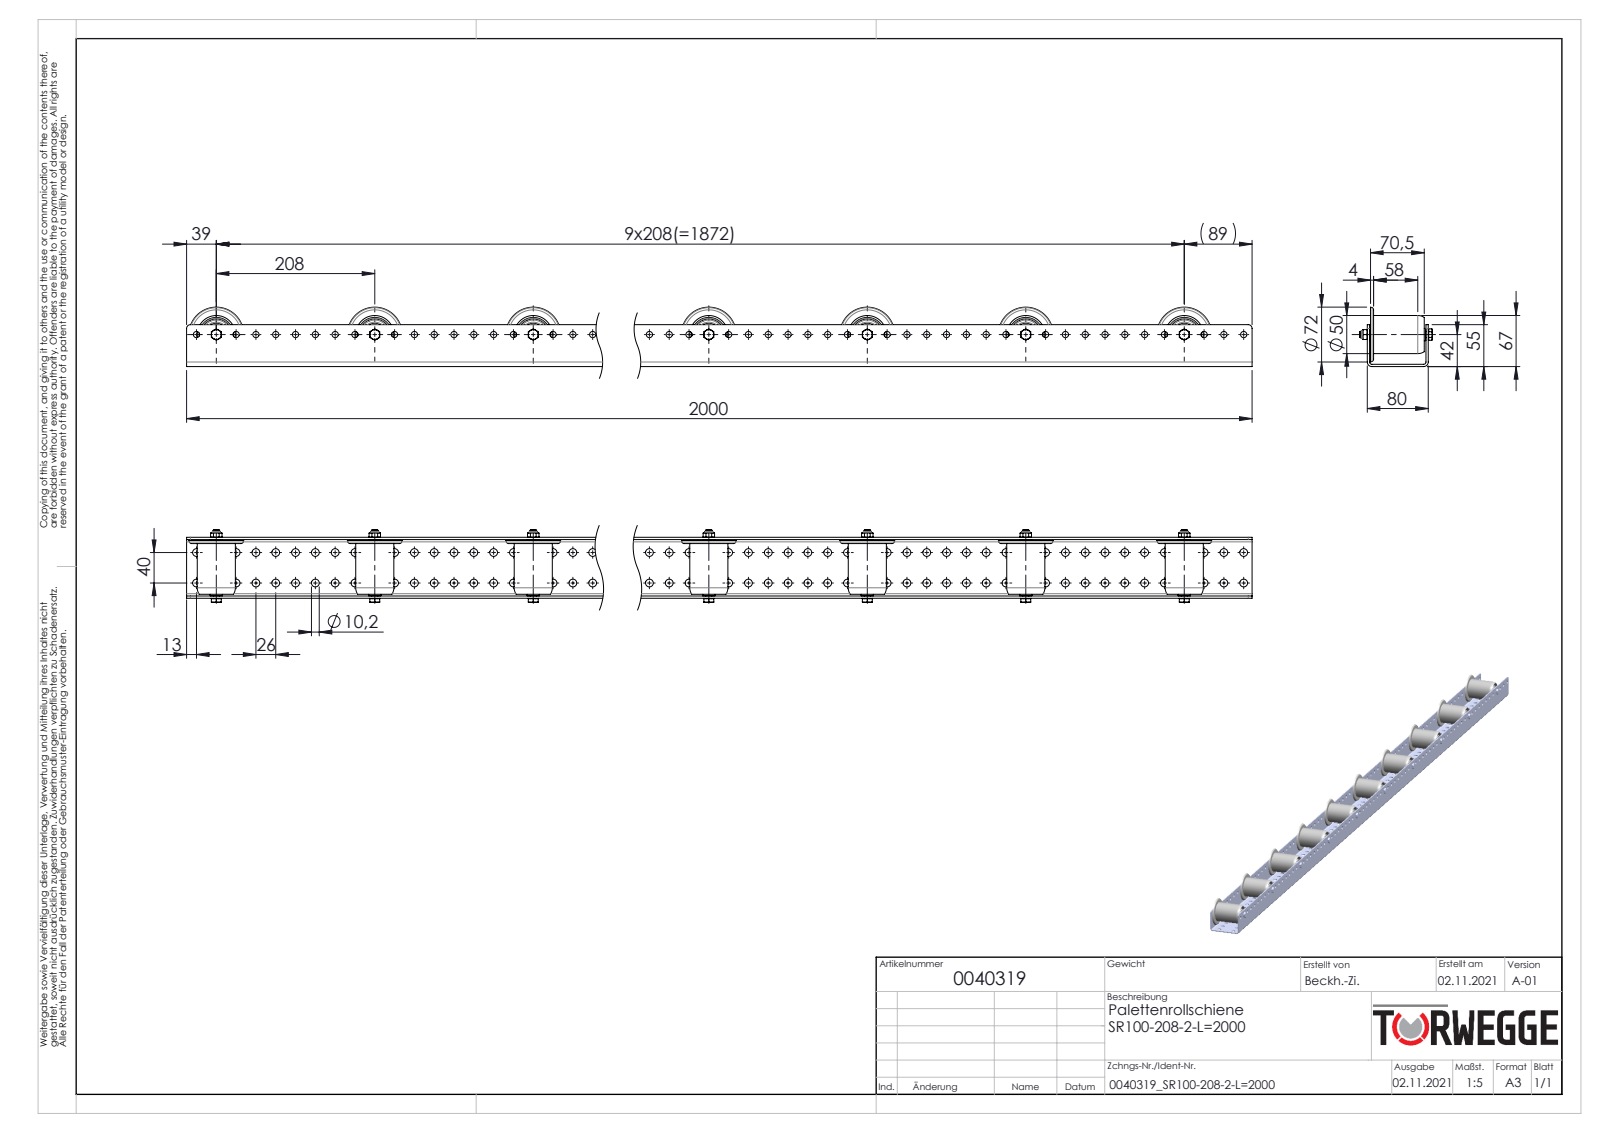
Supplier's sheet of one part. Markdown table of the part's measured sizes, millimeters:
| quantity | value |
| --- | --- |
| part name | 0040319 |
| STEP written by | SolidWorks 2020 (AUTOMOTIVE_DESIGN) |
| units | millimeters |
| bodies | 31 solids, 1864 faces (360 planar, 864 cylindrical, 640 other) |
| overall size | 2000 × 95.3 × 78 |
| volume | 2 302 000 mm³ |
| surface area | 999 830 mm² |
| round holes (diameter × count) | 10.2 × 154, 8.2 × 77, 6.8 × 10, 41 × 10, 45 × 10 |
| round bosses / shafts (diameter × count) | 50 × 10, 49.5 × 10, 29.5 × 10, 16 × 10, 13 × 10, 8 × 10 |
| partial cylindrical surfaces (radius × count) | 3 × 2, 5 × 2, 6 × 2 |
| main face-to-face distances | 3, 77, 80, 74, 1.5, 5.25, 71.75, 6.75, 3.75, 70.25 |
| hole center spacings | 26, 52, 78, 104, 130, 156, 182, 208 |
